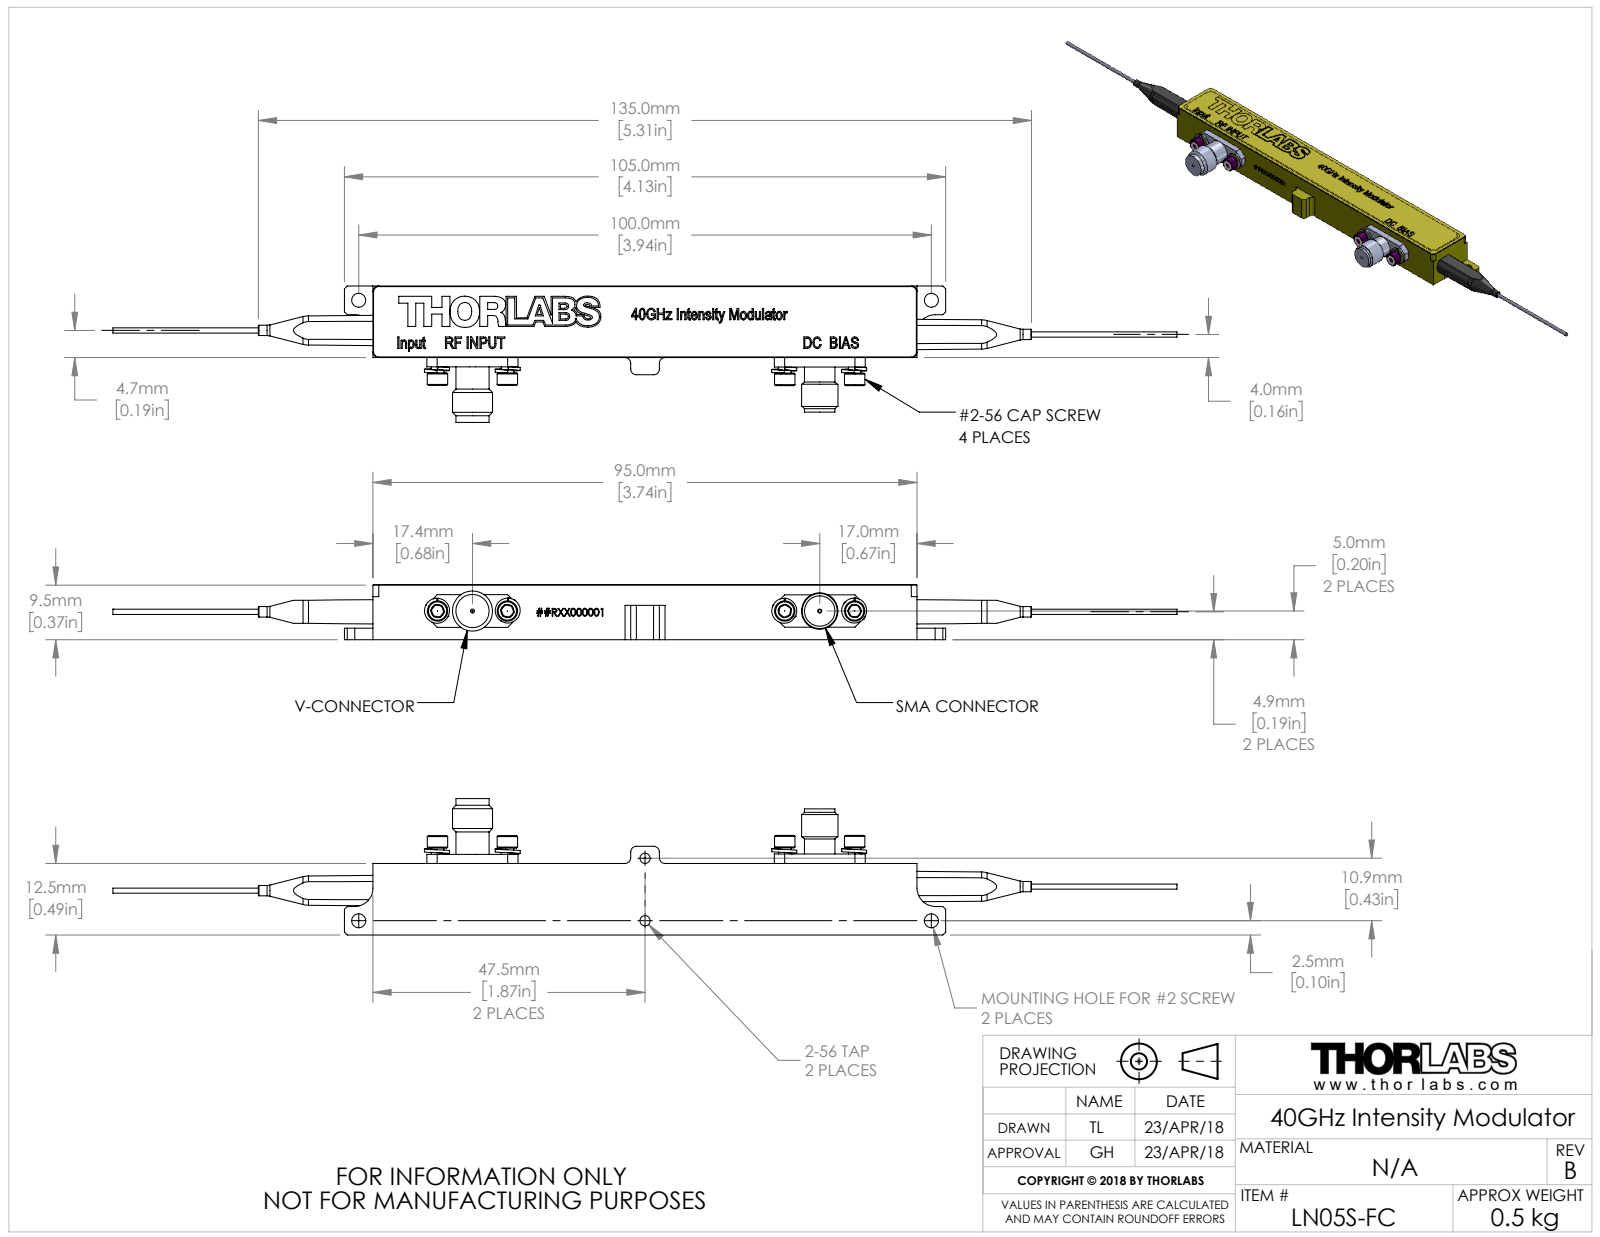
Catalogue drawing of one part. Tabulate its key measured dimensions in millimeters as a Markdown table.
| quantity | value |
| --- | --- |
| part name | 20869-E0W |
| STEP written by | SolidWorks 2016 (CONFIG_CONTROL_DESIGN) |
| units | millimeters |
| bodies | 0 solids, 605 faces (373 planar, 62 cylindrical, 170 other) |
| overall size | 185.8 × 23.81 × 9.63 |
| round holes (diameter × count) | 0.7 × 2, 1.78 × 2, 2.44 × 2 |
| round bosses / shafts (diameter × count) | 3.56 × 4, 2.18 × 4, 1.8 × 2, 0.9 × 2, 7 × 1, 6.35 × 1, 5.8 × 1, 5.31 × 1 |
| partial cylindrical surfaces (radius × count) | 1 × 8, 0.9 × 4, 3.18 × 2 |
| main face-to-face distances | 9.63, 12.5, 9.5, 9.58, 95, 1.65, 14.15, 7.58, 7.5, 14.1 |
| hole center spacings | 50, 51.17, 10.9, 60.64, 100 |
